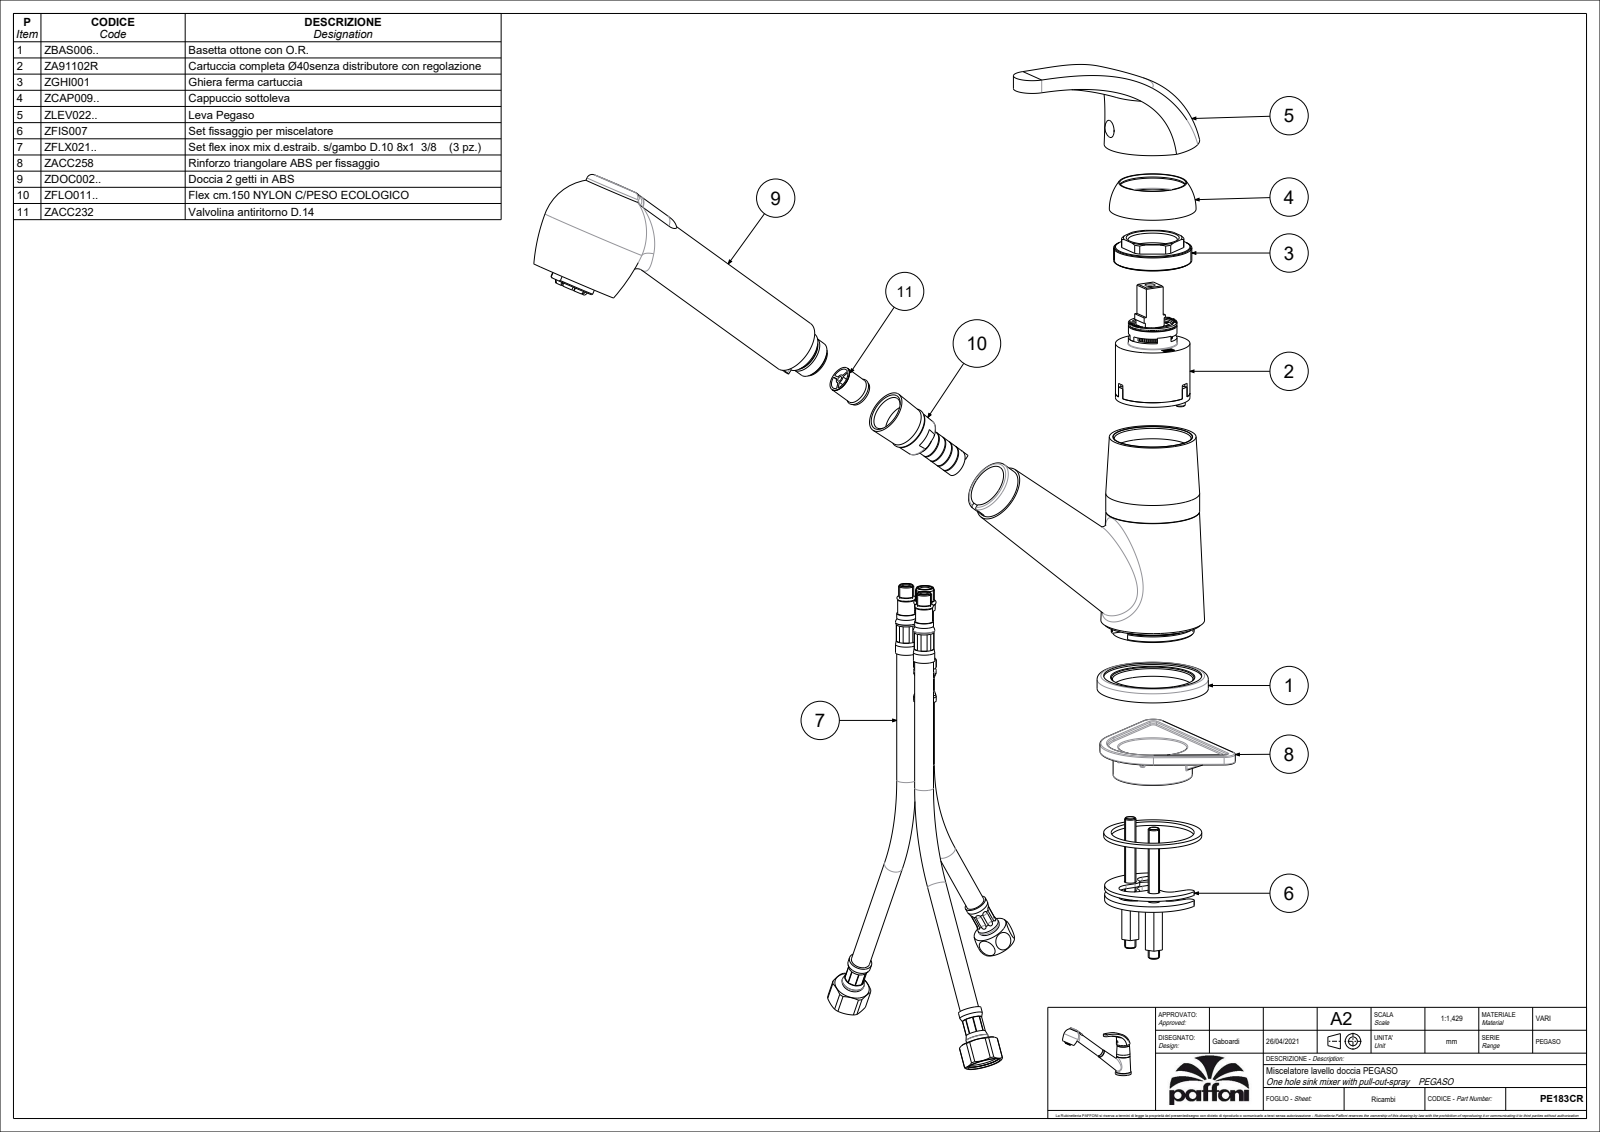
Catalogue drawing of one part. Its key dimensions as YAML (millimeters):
part_name: "PE183CR_SW0001"
step_written_by: "CREO PARAMETRIC BY PTC INC, 2022124 (CONFIG_CONTROL_DESIGN)"
units: millimeters
bodies: {solids: 2, faces: 433, planar: 126, cylindrical: 141, other: 166}
overall_size: [286.37, 204.49, 59]
volume: 377367
surface_area: 123159
round_holes:
  - {diameter: 7, count: 4}
  - {diameter: 5.25, count: 2}
  - {diameter: 5.5, count: 2}
  - {diameter: 8.6, count: 2}
  - {diameter: 9.4, count: 2}
  - {diameter: 6, count: 1}
  - {diameter: 7.5, count: 1}
  - {diameter: 9, count: 1}
  - {diameter: 11, count: 1}
  - {diameter: 14.2, count: 1}
  - {diameter: 16, count: 1}
  - {diameter: 21.5, count: 1}
round_bosses_or_shafts:
  - {diameter: 5, count: 2}
  - {diameter: 59, count: 1}
  - {diameter: 49.8, count: 1}
  - {diameter: 48.5, count: 1}
  - {diameter: 44.8, count: 1}
  - {diameter: 44, count: 1}
  - {diameter: 42, count: 1}
  - {diameter: 40, count: 1}
partial_cylinders:
  - {radius: 1, count: 8}
  - {radius: 0.56, count: 7}
  - {radius: 12.5, count: 3}
  - {radius: 8, count: 2}
  - {radius: 1.9, count: 1}
  - {radius: 2, count: 1}
  - {radius: 3.9, count: 1}
  - {radius: 12, count: 1}
face_to_face_distances: [1, 122.57, 0.97, 74.6, 74.57, 73.6, 67.1, 7.5, 122.54, 121.57]
hole_center_spacings: [6.04, 9.96, 10.51, 11.24, 11.4, 12.01, 12.26, 14.09]
